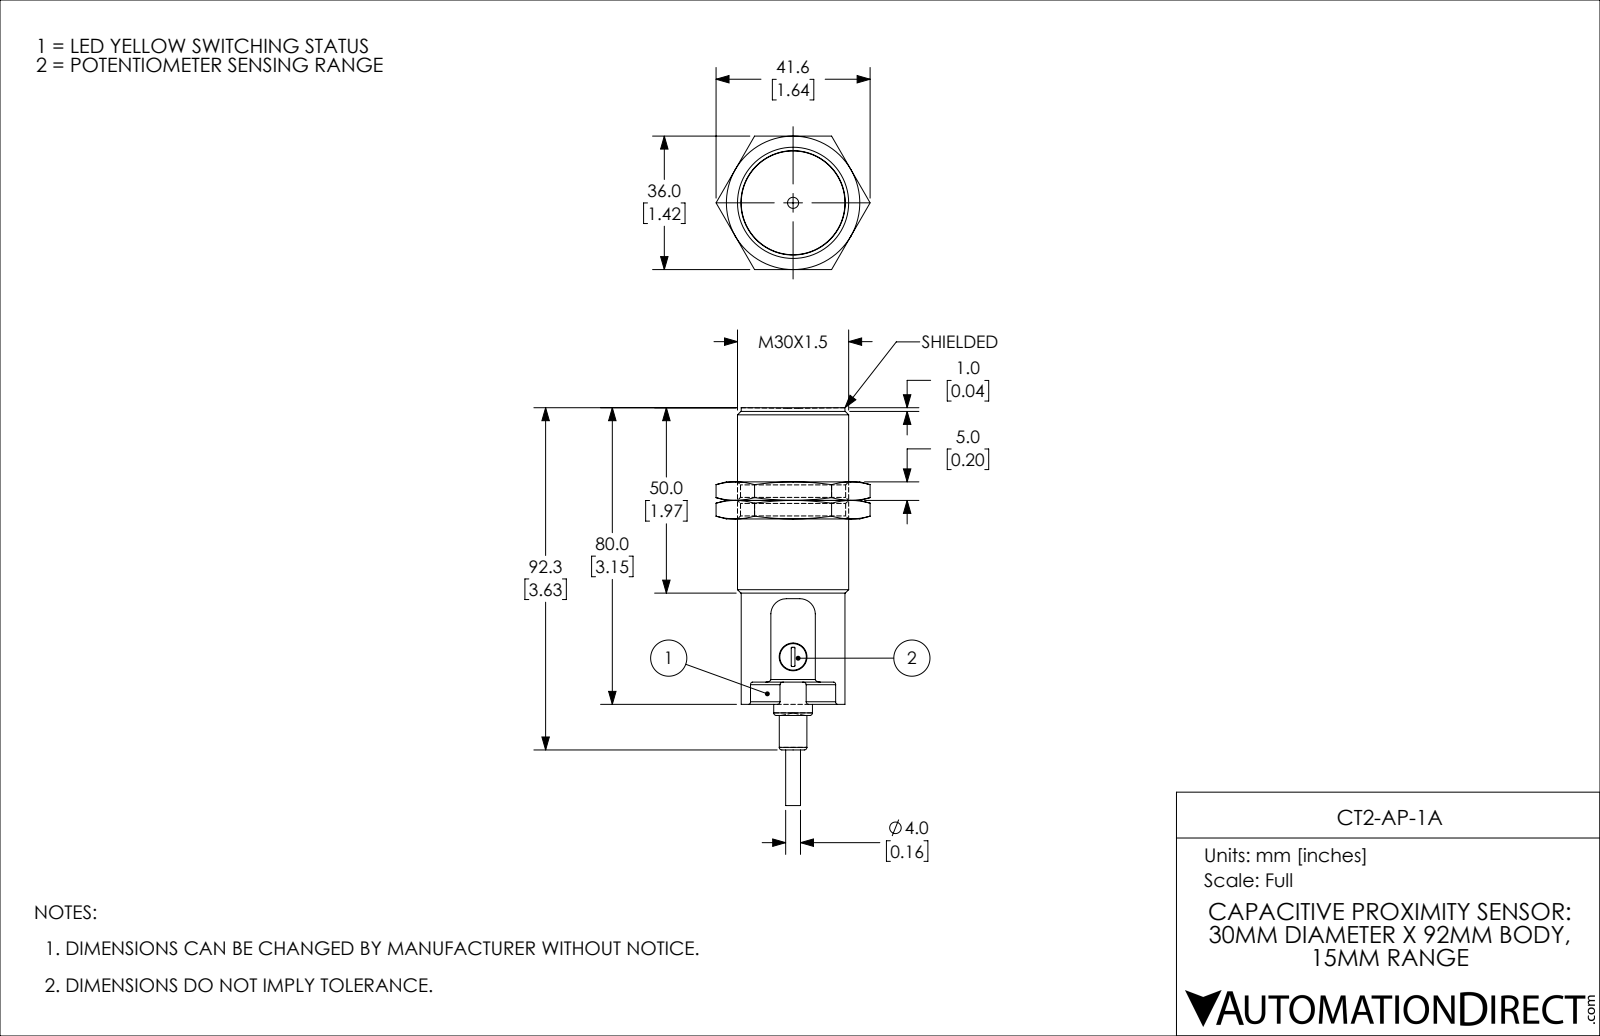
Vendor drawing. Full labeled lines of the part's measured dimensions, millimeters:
Part name (STEP PRODUCT): CT2-AN-2A
STEP written by: SolidWorks 2018 (AUTOMOTIVE_DESIGN)
Units: millimetres
Bodies: 3 solids, 88 faces (33 planar, 20 cylindrical, 35 other)
Overall size (bounding box): 107.3 × 41.6 × 36
Volume: 58 390 mm³ · Surface area: 12 940 mm²
Round holes (diameter × count): ⌀28.4 ×1
Round bosses / shafts (diameter × count): ⌀30 ×1, ⌀28 ×1, ⌀10.4 ×1, ⌀7.5 ×1, ⌀7.4 ×1, ⌀4 ×1
Partial cylindrical surfaces — rounded edges, fillets, slot ends (radius × count): R0.2 ×4, R0.7 ×3, R4.2 ×2
Main face-to-face distances: 5, 36, 55, 10, 50, 60, 30.7, 5.4, 26, 4.6
